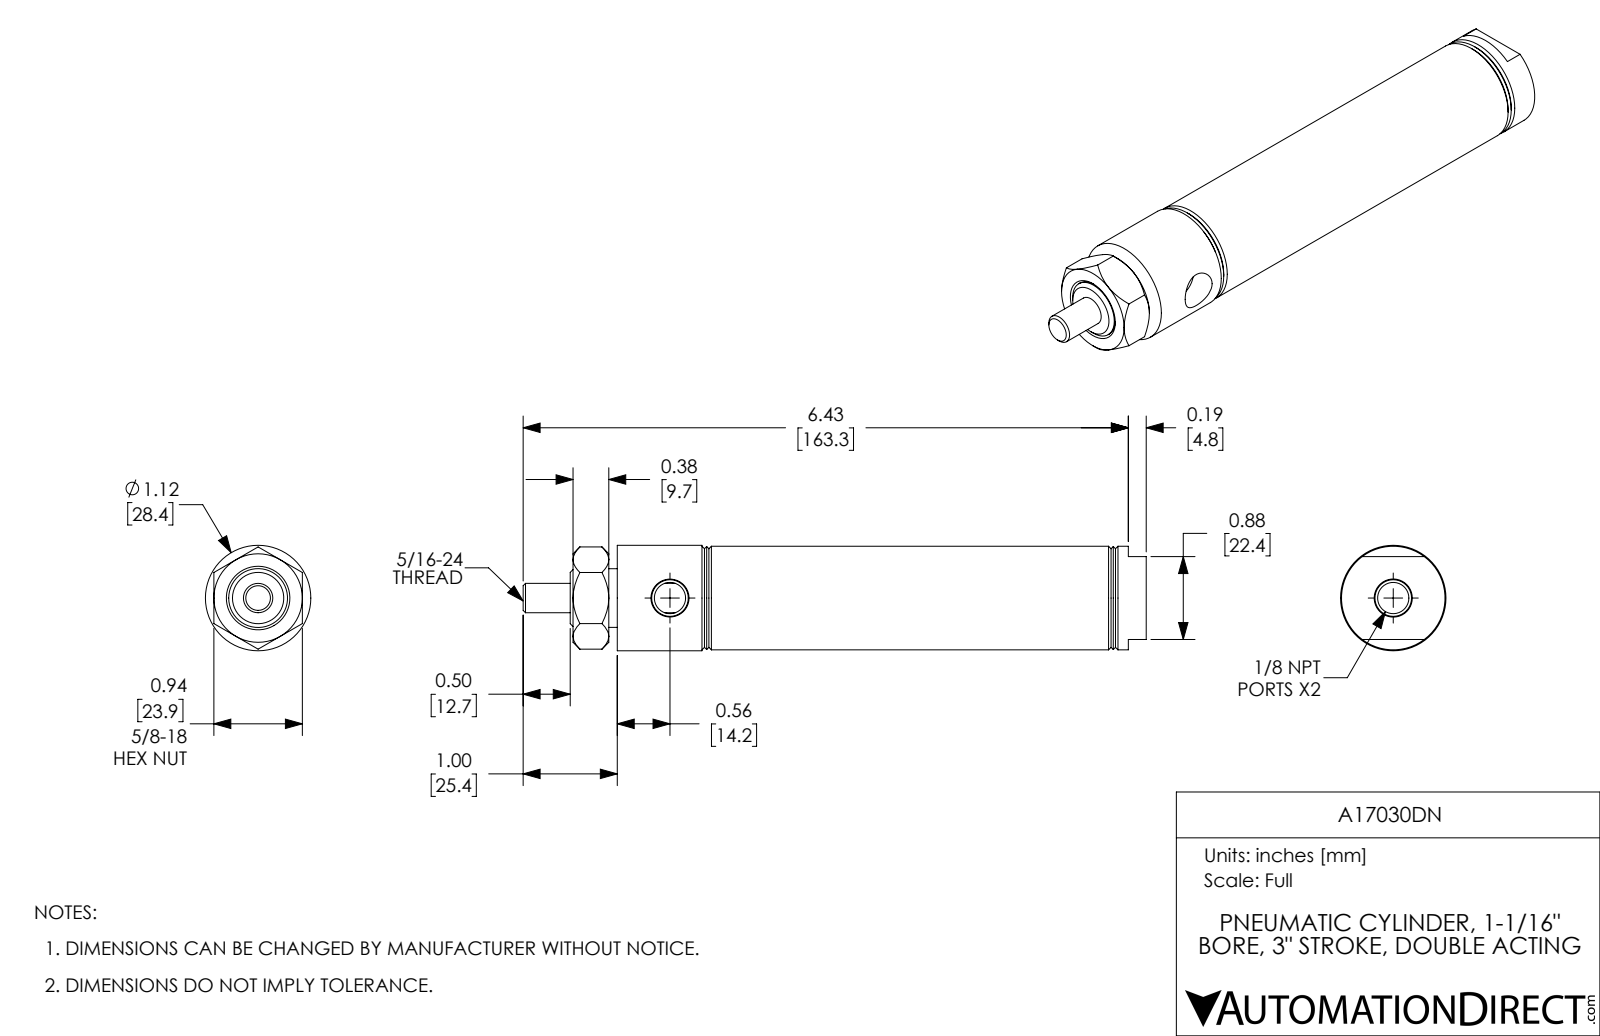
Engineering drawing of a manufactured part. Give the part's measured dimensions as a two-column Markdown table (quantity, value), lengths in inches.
| quantity | value |
| --- | --- |
| part name | A17030DN; A17030DN_Mounting Nut_D-9; A17030DN-Rod; A17030DN-MainBody |
| STEP written by | SolidWorks 2017 (AUTOMOTIVE_DESIGN) |
| units | inches |
| bodies | 3 solids, 94 faces (24 planar, 26 cylindrical, 44 other) |
| overall size | 6.62 × 1.12 × 1.12 |
| volume | 3.14 in³ |
| surface area | 49.83 in² |
| round holes (diameter × count) | 0.332 × 2, 0.312 × 1, 0.625 × 1, 1.063 × 1 |
| round bosses / shafts (diameter × count) | 1.12 × 1, 1.1 × 1, 0.623 × 1 |
| main face-to-face distances | 0.5, 4.56, 3.5, 3, 1.06, 1.56, 4.56, 5.62, 4.06, 1.06 |
